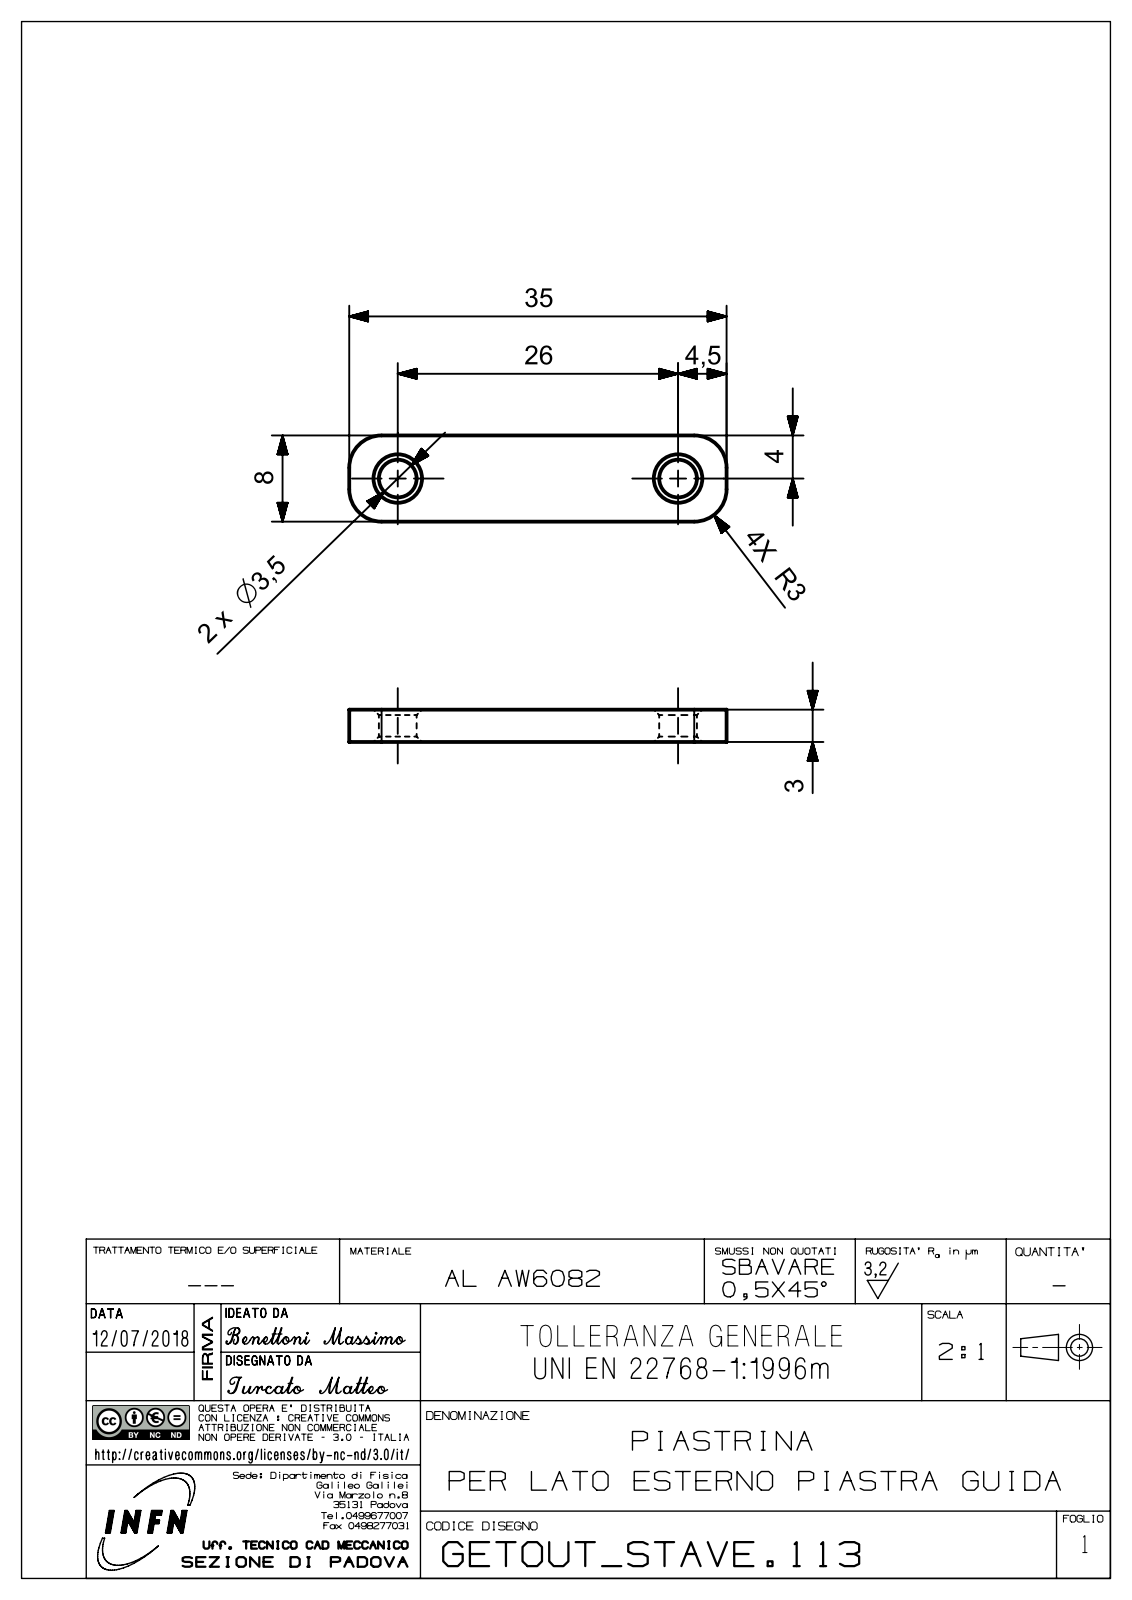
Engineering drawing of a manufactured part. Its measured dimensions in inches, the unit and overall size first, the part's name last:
Units: inches
Overall size (bounding box): 1.378 × 0.315 × 0.118
Round holes (diameter × count): ⌀0.138 ×2
Partial cylindrical surfaces — rounded edges, fillets, slot ends (radius × count): R0.118 ×4
Main face-to-face distances: 0.118, 0.315, 1.378
Hole centre spacings: 1.024
Volume: 0.046 in³ · Surface area: 1.24 in²
Bodies: 1 solid, 16 faces (6 planar, 6 cylindrical, 4 other)
Part name (STEP PRODUCT): bezA730AE56cd1w
STEP written by: SIEMENS PLM Software NX 12.0 (AUTOMOTIVE_DESIGN)
